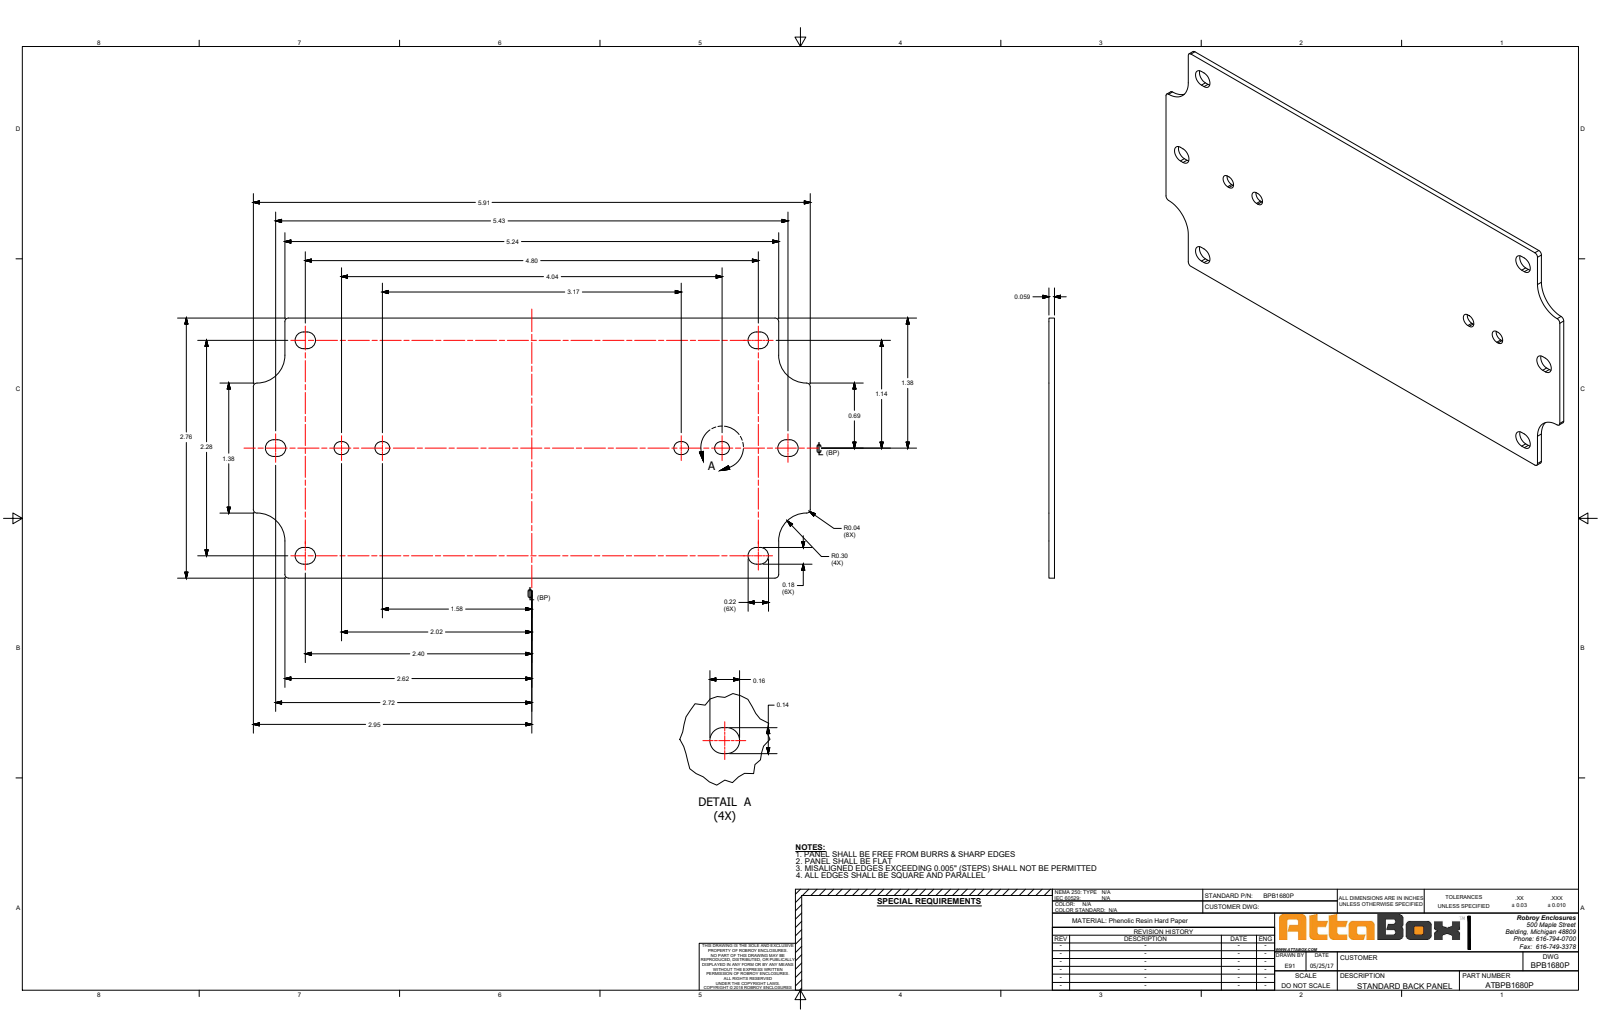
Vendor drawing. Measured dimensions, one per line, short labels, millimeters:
name: BPB1680P
written by: SolidWorks 2018 (AUTOMOTIVE_DESIGN)
unit: mm
bodies: 1 solid, 62 faces (30 planar, 32 cylindrical, 0 other)
size: 150 × 70 × 1.5
volume: 14 700 mm³; area: 20 420 mm²
rounds: 12× R2.3, 8× R1, 8× R1.8, 4× R7.5
face distances: 1.5, 70, 8.5, 141.5, 150, 133, 29, 4.5, 8.3, 61.7
